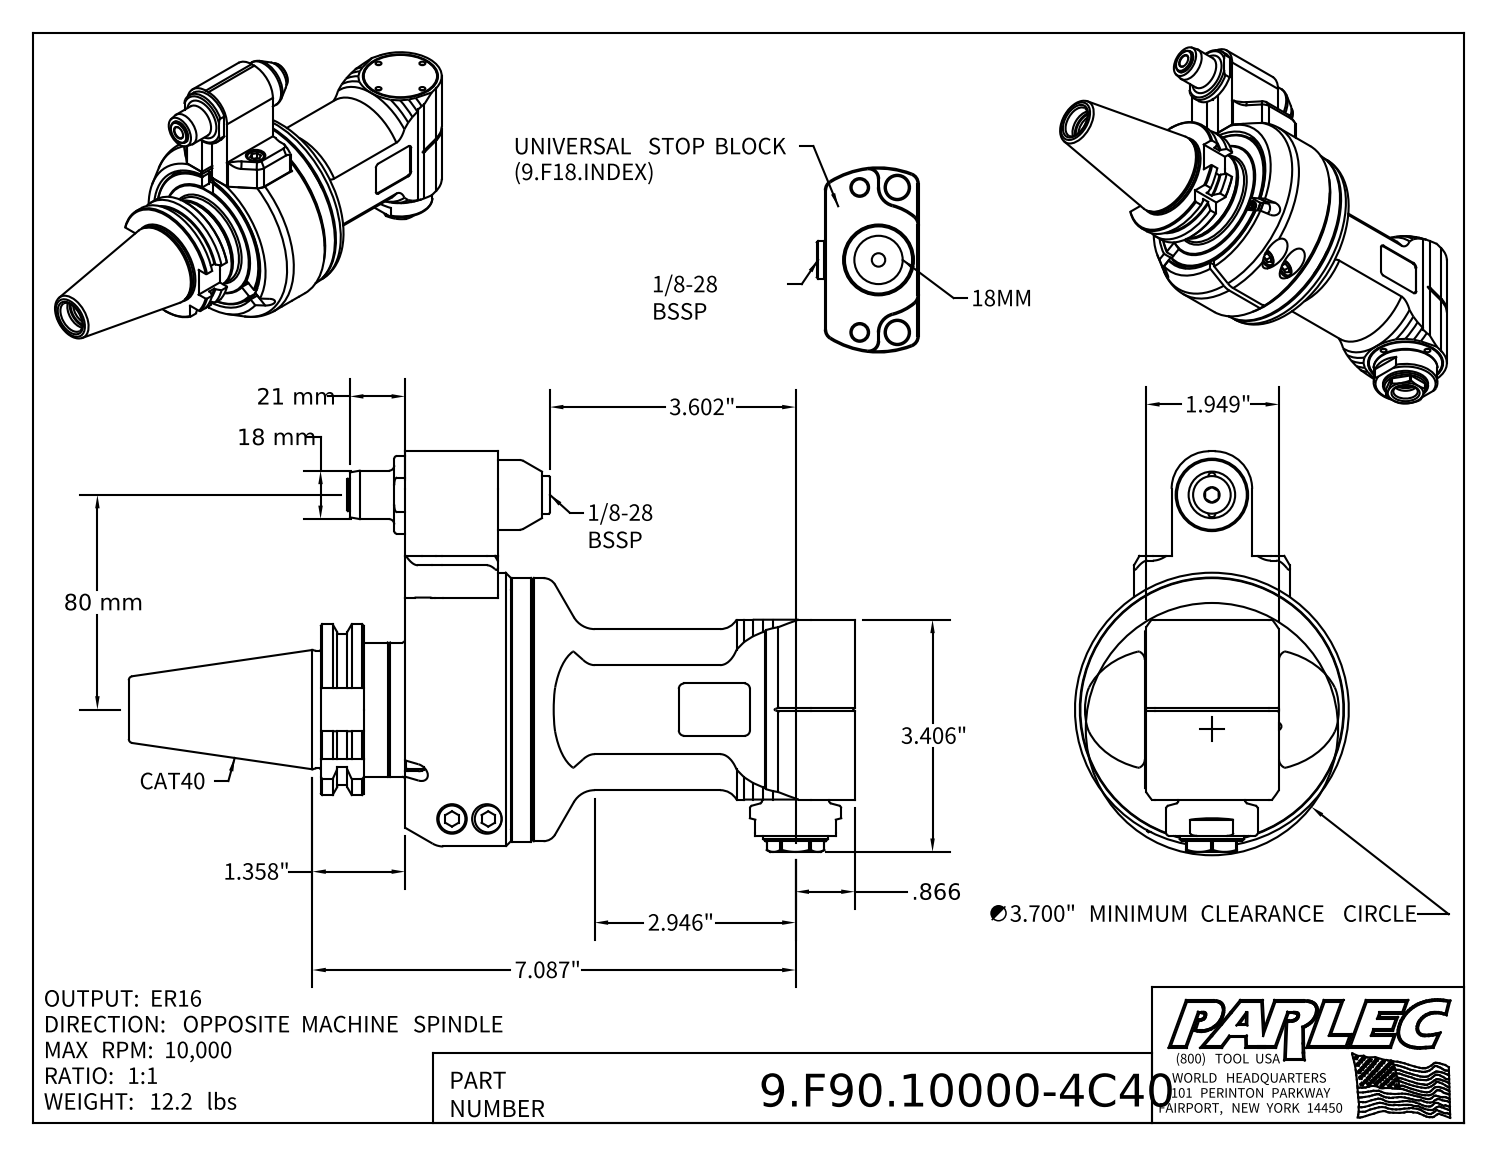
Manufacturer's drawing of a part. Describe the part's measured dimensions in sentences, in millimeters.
The part is named "9.F90.10000-4C40; 9_F90_10000; 9_GA1_148_2 (Type 1, Cat40, 80mm)". Its 3-D file was written by "Autodesk Inventor 2022 (AUTOMOTIVE_DESIGN)". It is 5 solids with 625 faces: 265 planar, 162 cylindrical and 198 other. Overall it measures 270.4 by 149.3 by 102 millimeters. Its volume is 922 600 cubic millimeters and its surface area 150 700 square millimeters. Round holes: 20 of diameter 8.5, 4 of diameter 1.6, 4 of diameter 2, 4 of diameter 3.2, 3 of diameter 11, 2 of diameter 2.6, 2 of diameter 4.2, 2 of diameter 5, 2 of diameter 10.4, 2 of diameter 12, 2 of diameter 13, 1 of diameter 2.5. Round bosses or shafts: 4 of diameter 10, 4 of diameter 6, 2 of diameter 18, 2 of diameter 8, 2 of diameter 2.5, 1 of diameter 102, 1 of diameter 98.4, 1 of diameter 98. Partial cylindrical surfaces (rounded edges, fillets, slot ends): 12 of radius 2, 4 of radius 4, 2 of radius 0.4, 2 of radius 0.5, 2 of radius 1, 2 of radius 3.5, 2 of radius 5, 2 of radius 6. The main face-to-face distances are 32, 39.5, 0.5, 8.5, 7.5, 7, 26, 10, 1, 50. The hole center spacings are 38.5, 37.3, 46.3, 54.5, 67.3, 76.3, 10.7, 58.2.
